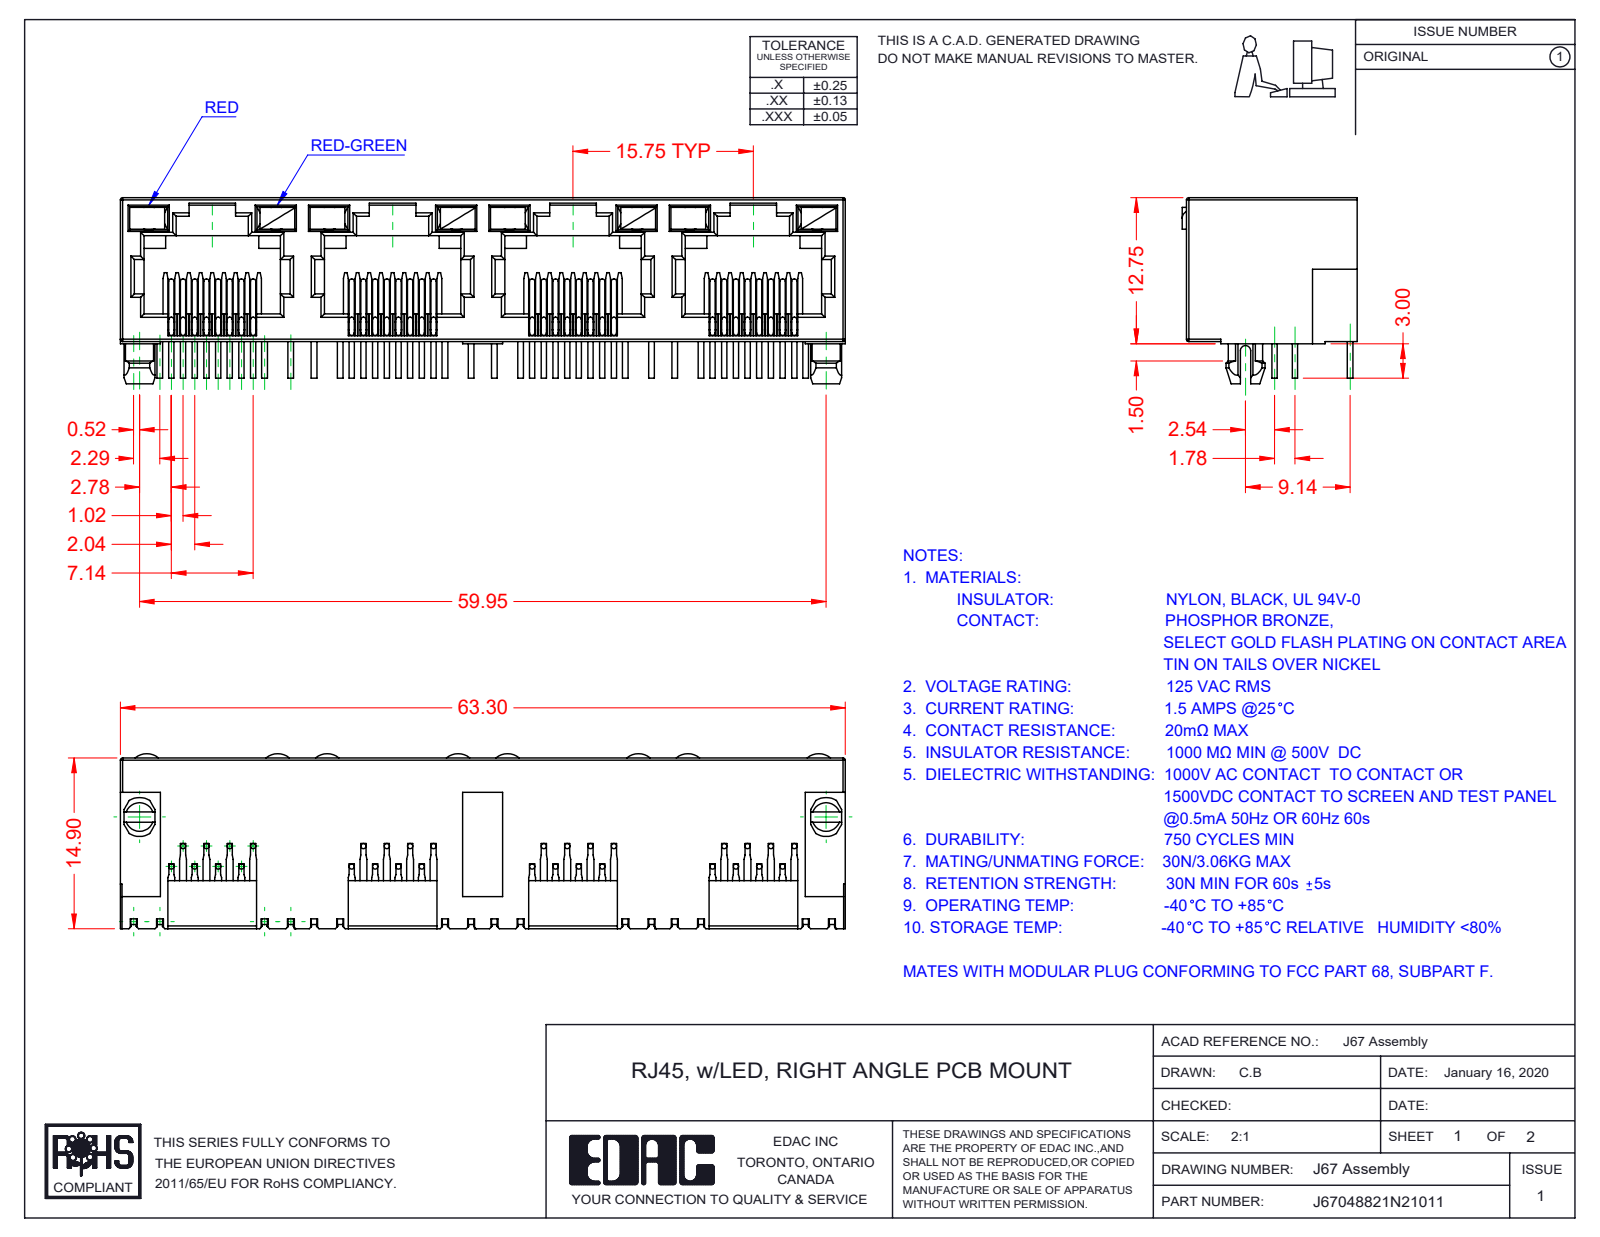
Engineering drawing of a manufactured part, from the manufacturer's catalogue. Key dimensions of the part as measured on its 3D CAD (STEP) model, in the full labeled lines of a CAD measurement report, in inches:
Part name (STEP PRODUCT): J67048822N26011; 67 LED RH_6-Red-Green; 67 LED LH_2-Red; 67 Contacts (+1 more)
STEP written by: SolidWorks 2016 (CONFIG_CONTROL_DESIGN)
Units: inches
Bodies: 41 solids, 2473 faces (1781 planar, 484 cylindrical, 208 other)
Overall size (bounding box): 2.492 × 0.64 × 0.602
Volume: 0.315 in³ · Surface area: 17.94 in²
Round bosses / shafts (diameter × count): ⌀0.018 ×96
Partial cylindrical surfaces — rounded edges, fillets, slot ends (radius × count): R0.008 ×66, R0.012 ×29, R0.018 ×9, R0.061 ×8, R0.059 ×2, R0.067 ×2, R0.014 ×1, R0.039 ×1
Main face-to-face distances: 0.02, 0.494, 0.074, 0.035, 0.394, 0.62, 0.039, 0.055, 0.433, 0.468
